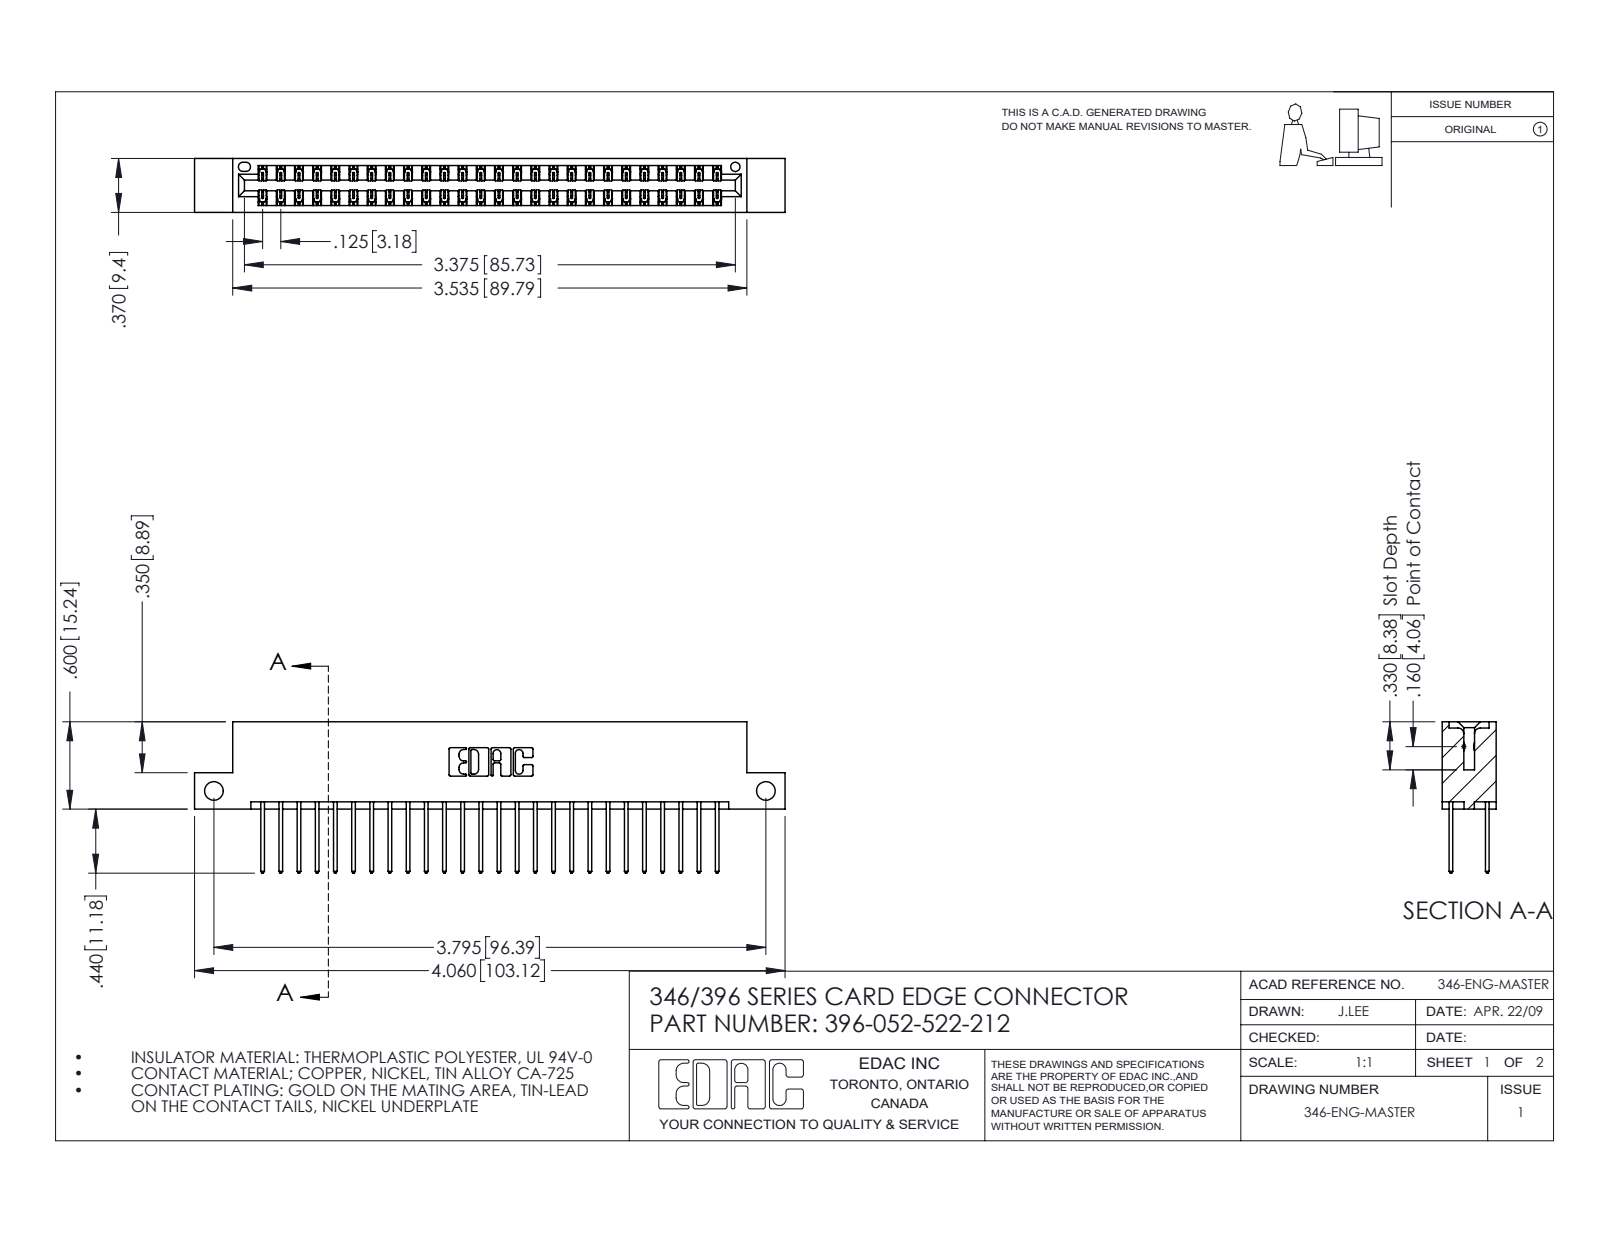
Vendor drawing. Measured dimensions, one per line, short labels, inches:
name: 396-052-522-212; 346 Part_Flush Mounting Lugs - Side Mount; 345-292-001_345-293-122
written by: SolidWorks 2016 (CONFIG_CONTROL_DESIGN)
unit: in
bodies: 53 solids, 2826 faces (1896 planar, 930 cylindrical, 0 other)
size: 4.06 × 1.04 × 0.37
volume: 0.609 in³; area: 21.61 in²
holes: 2× ⌀0.128, 1× ⌀0.064
rounds: 78× R0.006, 52× R0.01, 22× R0.01, 6× R0.007, 6× R0.031, 3× R0.026, 2× R0.014, 2× R0.022
face distances: 0.048, 0.322, 0.25, 0.37, 0.072, 0.298, 0.025, 0.275, 0.148, 0.222
hole spacings: 3.795
